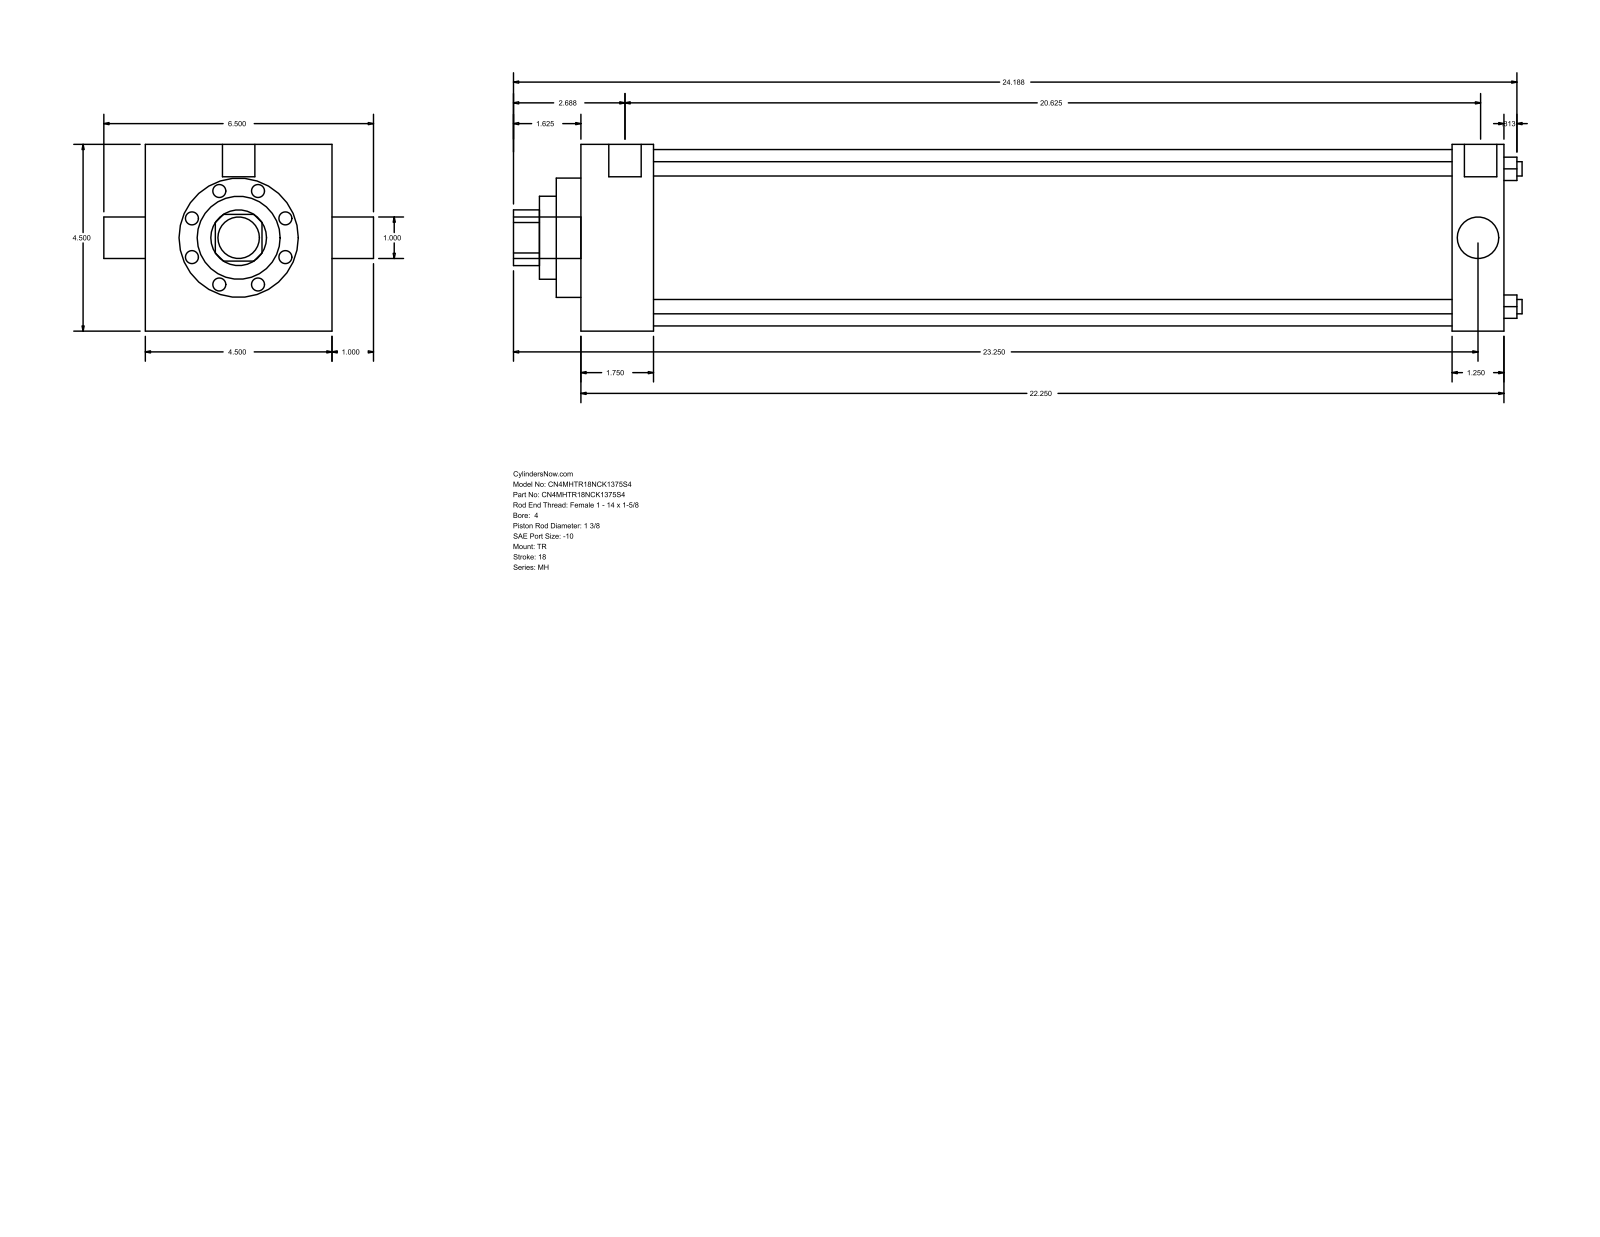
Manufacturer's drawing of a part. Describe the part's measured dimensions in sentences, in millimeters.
The part is named "MH_TR__0400_1.375". Its 3-D file was written by "GSSL Pune (CONFIG_CONTROL_DESIGN)". It is 0 solids with 86 faces: 61 planar, 25 cylindrical and 0 other. Overall it measures 617.54 by 165.1 by 114.3 millimeters. Round holes: 4 of diameter 8.76, 1 of diameter 25.4, 1 of diameter 34.92, 1 of diameter 50.8, 1 of diameter 73.03, 1 of diameter 107.95. Round bosses or shafts: 3 of diameter 8.73, 2 of diameter 19.84, 1 of diameter 25.4. Partial cylindrical surfaces (rounded edges, fillets, slot ends): 1 of radius 17.06. The main face-to-face distances are 114.3, 565.15, 44.45, 520.7, 533.4, 488.95, 31.75, 15.08, 59.53, 548.48. The hole center spacings are 59.62, 84.32, 119.25.
